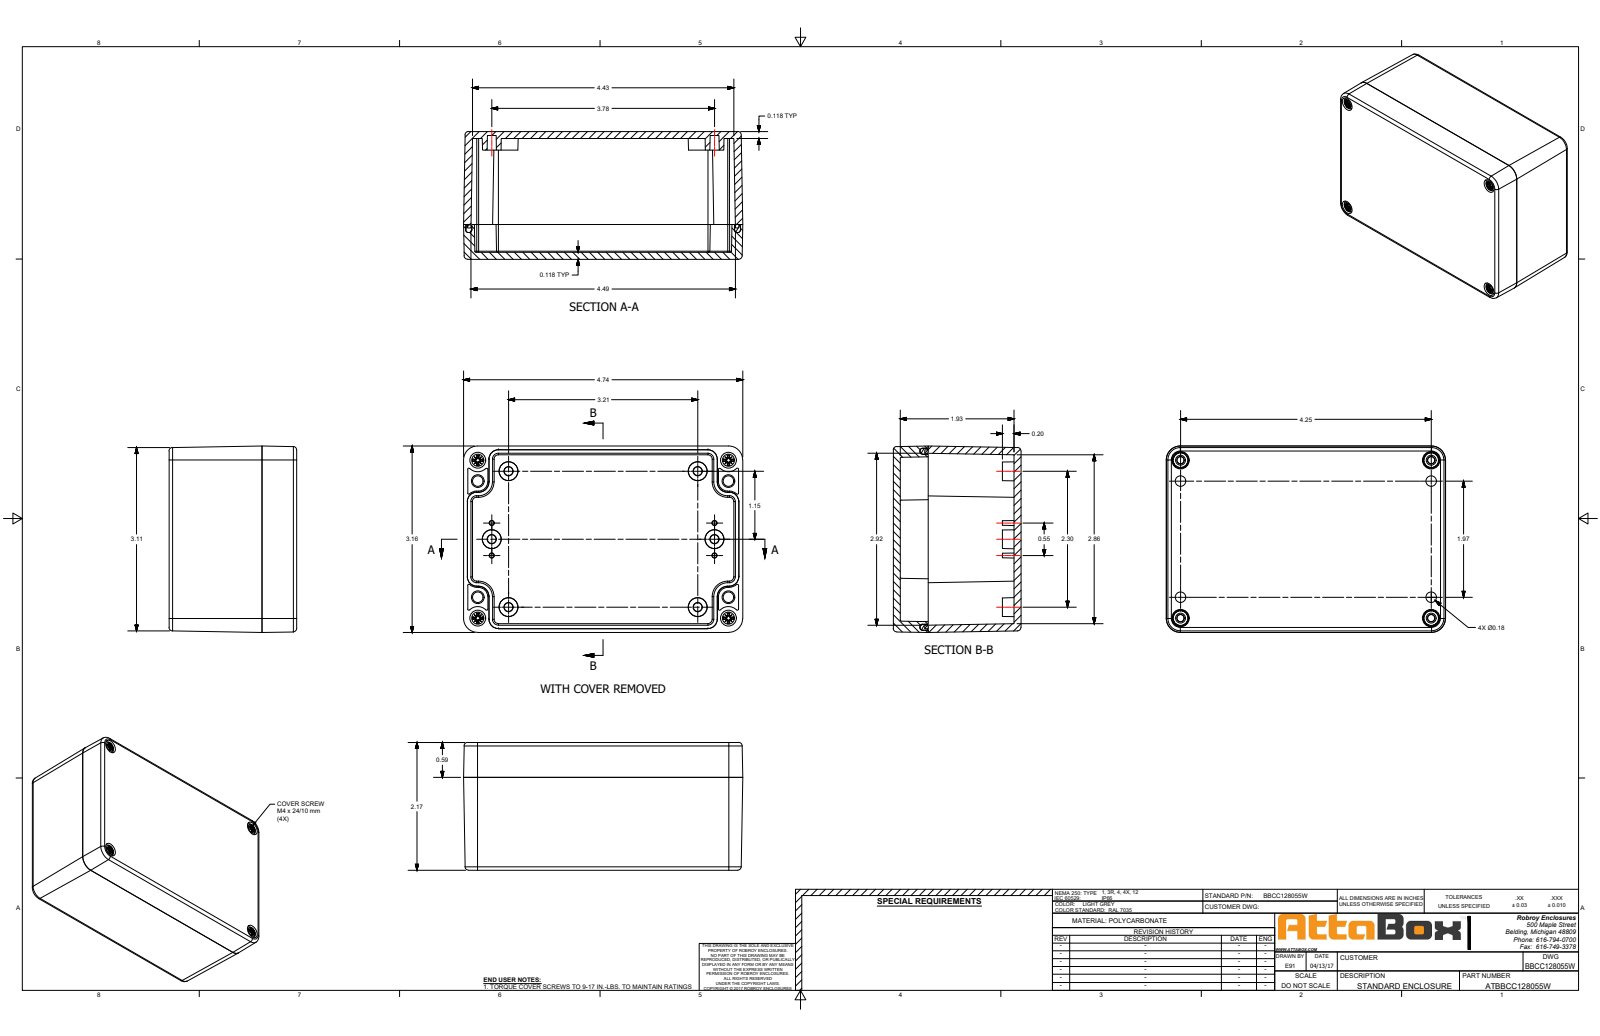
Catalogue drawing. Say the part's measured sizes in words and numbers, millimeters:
The part is named "BBCC128055W". Its 3-D file was written by "SolidWorks 2018 (AUTOMOTIVE_DESIGN)". It is 11 solids with 1632 faces: 611 planar, 431 cylindrical and 590 other. Overall it measures 120.3 by 80.3 by 55 millimeters. Its volume is 136 200 cubic millimeters and its surface area 98 710 square millimeters. Round holes: 8 of diameter 4.5, 4 of diameter 3.3, 4 of diameter 4.8, 4 of diameter 5.1, 4 of diameter 7, 4 of diameter 7.4, 4 of diameter 7.5. Round bosses or shafts: 4 of diameter 6.8, 4 of diameter 4.4, 4 of diameter 4, 4 of diameter 3.3. Partial cylindrical surfaces (rounded edges, fillets, slot ends): 35 of radius 0.5, 32 of radius 1.1, 16 of radius 1, 8 of radius 1.5, 8 of radius 2.1, 8 of radius 4.7, 4 of radius 2.6, 4 of radius 2.8. The main face-to-face distances are 3, 52, 55, 49, 3.1, 80.3, 77.1, 4.6, 3.2, 12. The hole center spacings are 9, 59, 108, 108.4, 123.1, 50, 68, 119.
